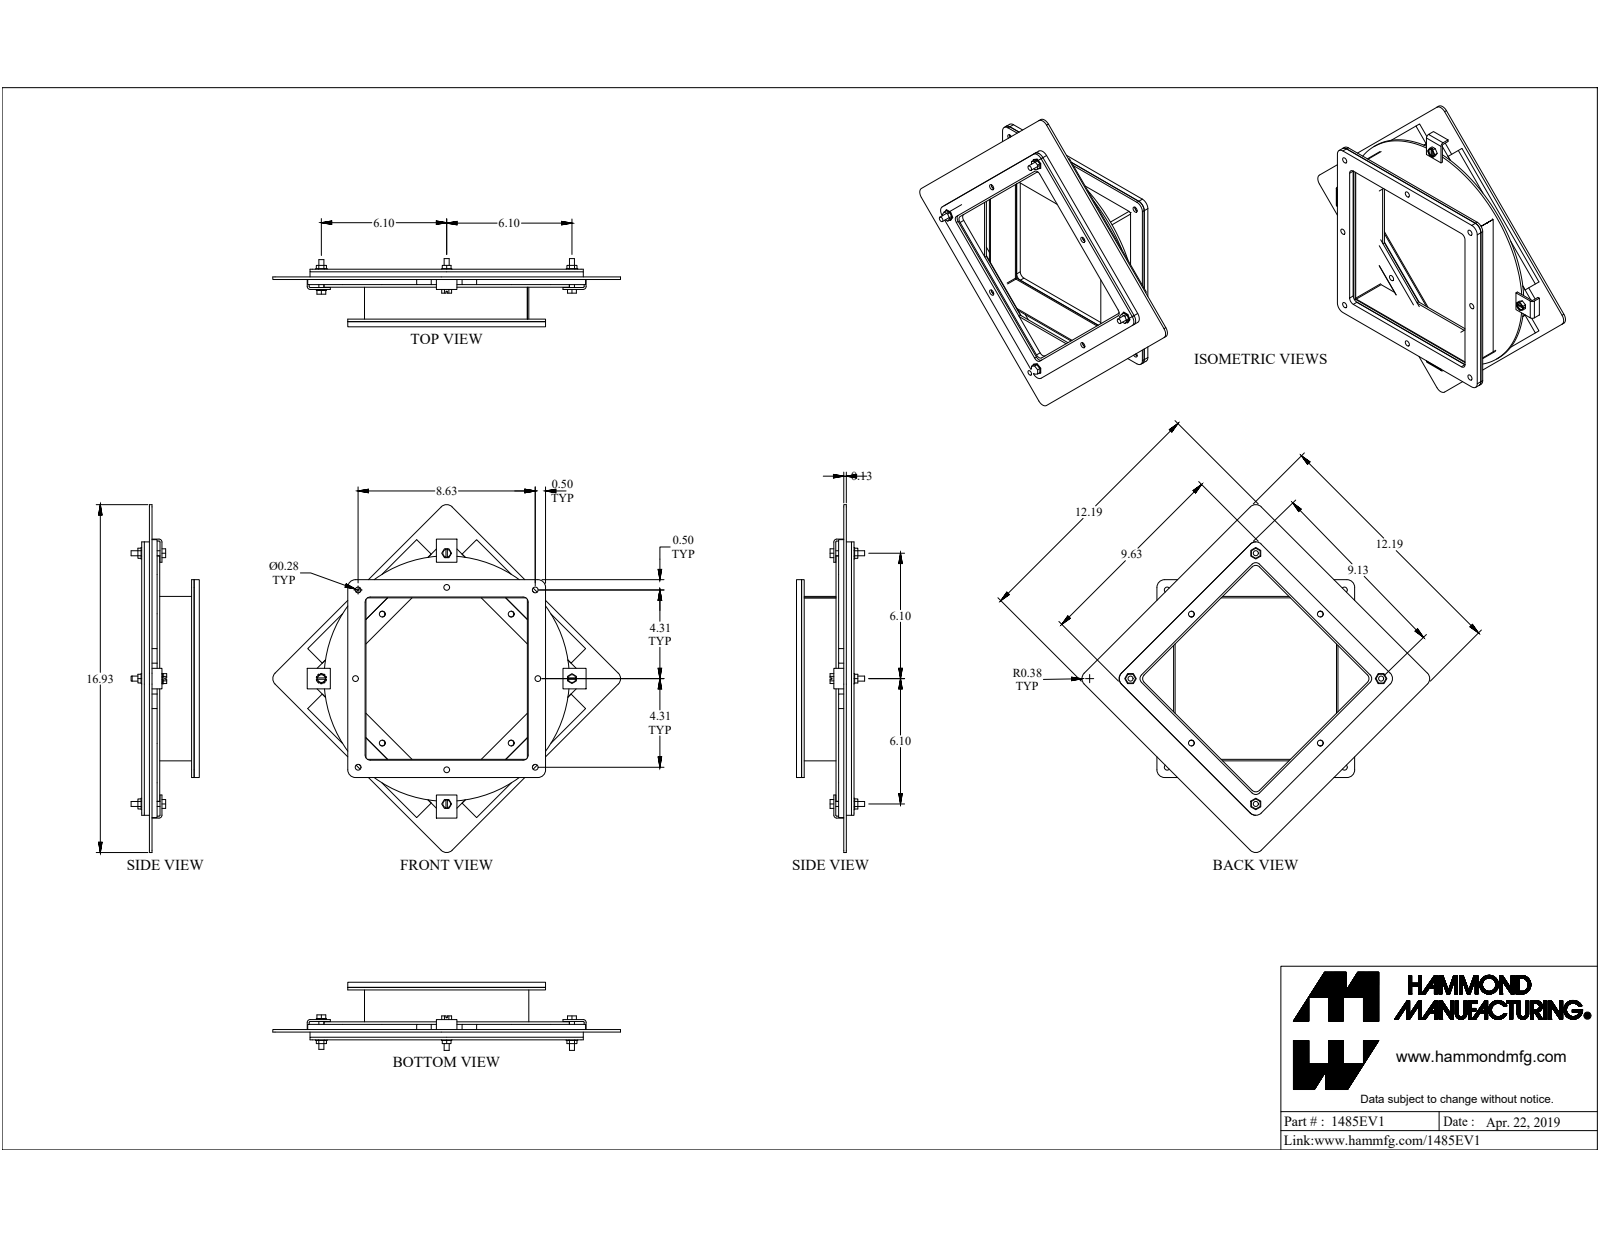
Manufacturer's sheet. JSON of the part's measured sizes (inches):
{"part_name": "1485EV1", "step_written_by": "SolidWorks 2019 (CONFIG_CONTROL_DESIGN)", "units": "inches", "bodies": {"solids": 35, "faces": 574, "planar": 391, "cylindrical": 167, "other": 16}, "overall_size": [16.925, 16.925, 3.317], "volume_in3": 61.55, "surface_area_in2": 934.4, "round_holes": [[0.281, 24], [0.375, 6], [0.196, 5], [0.312, 4], [0.187, 2], [0.265, 2], [0.313, 2], [0.224, 1], [0.258, 1]], "round_bosses_or_shafts": [[0.244, 5], [0.563, 2], [0.25, 2], [11.937, 1]], "partial_cylinders_radius": [[0.375, 16], [0.25, 13], [0.048, 9], [0.143, 9], [0.062, 4], [0.036, 3], [0.108, 3], [0.06, 1]], "face_to_face_distances": [0.25, 0.375, 0.125, 0.125, 2.426, 0.375, 2.051, 1.676, 0.75, 0.5], "hole_center_spacings": [9.755, 4.314, 4.315, 6.276, 7.543, 8.625, 7.542, 3.396]}
